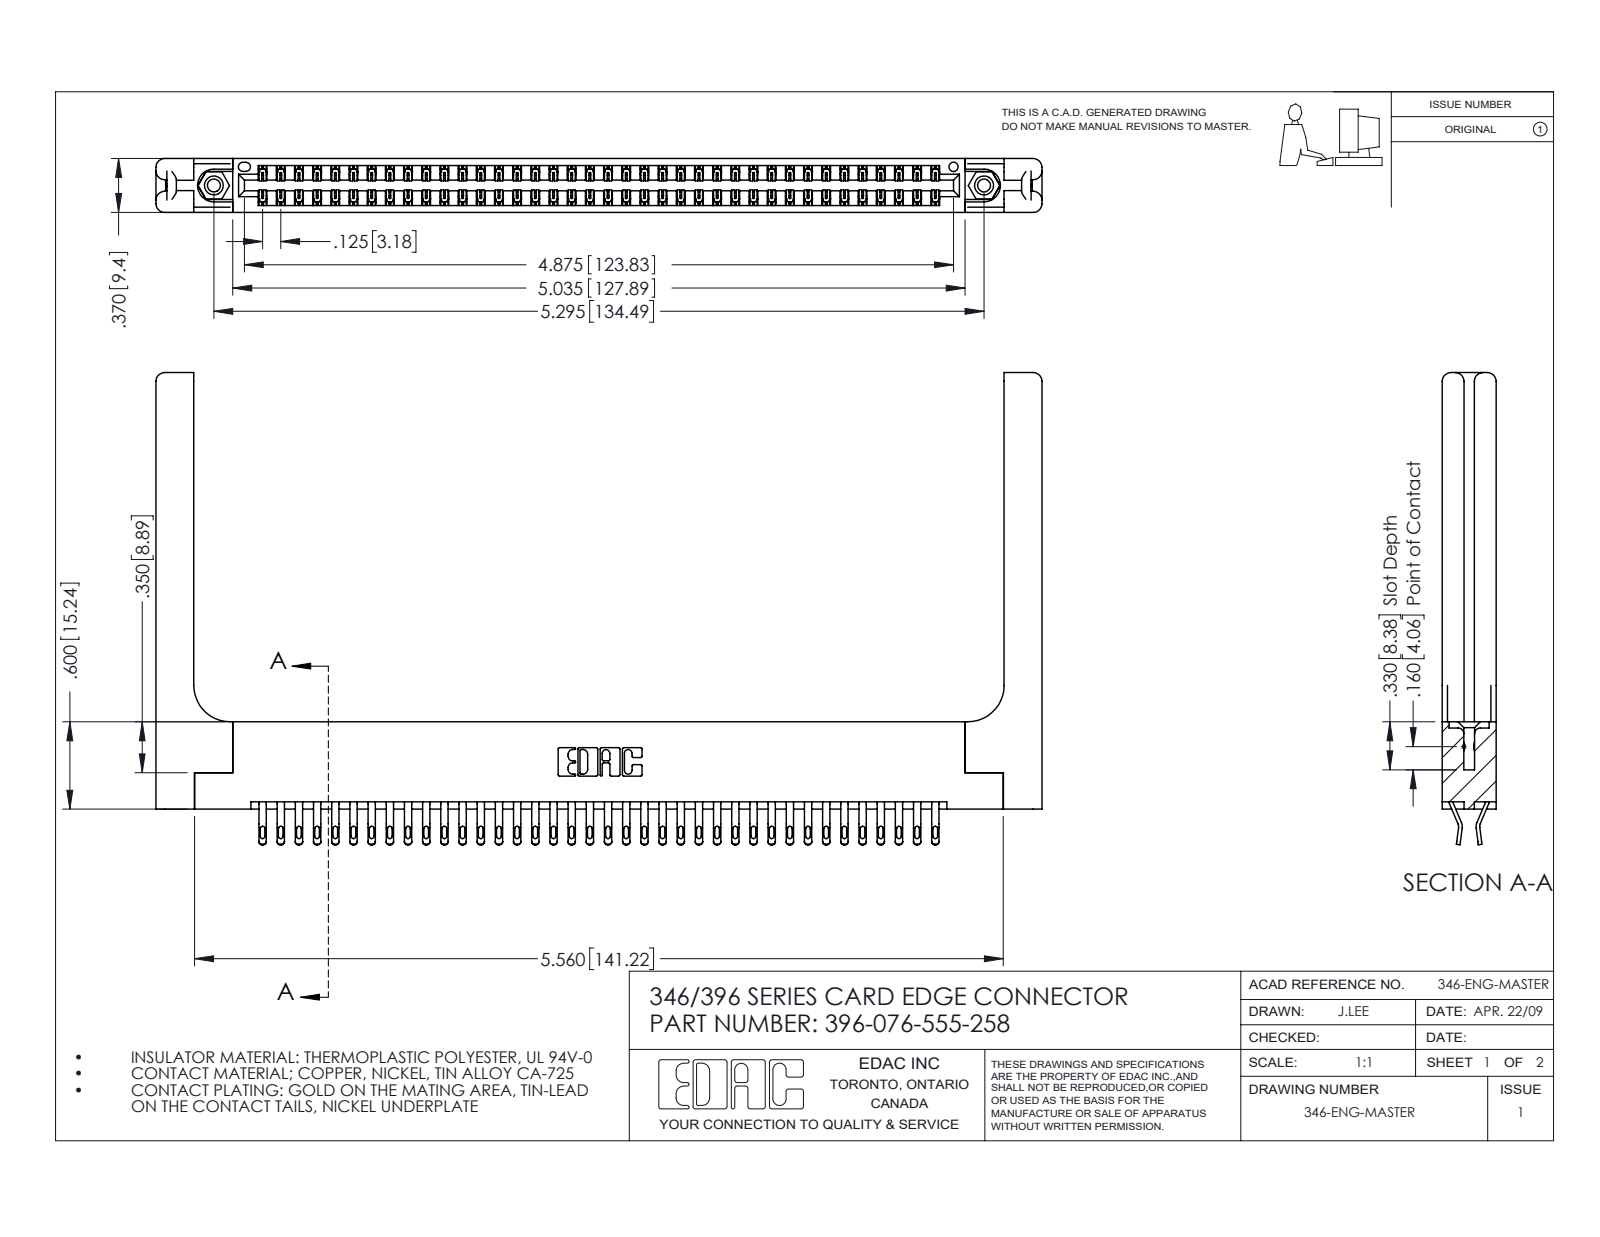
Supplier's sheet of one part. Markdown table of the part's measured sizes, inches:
| quantity | value |
| --- | --- |
| part name | 396-076-555-258; 345-250-001_345-250-001-102; 345-292-001_555 Tail; 346 Part_Flush Mounting Lugs - 0.156 Dia-TH (+1 more) |
| STEP written by | SolidWorks 2016 (CONFIG_CONTROL_DESIGN) |
| units | inches |
| bodies | 81 solids, 4786 faces (2732 planar, 1994 cylindrical, 60 other) |
| overall size | 6.091 × 3.245 × 0.37 |
| volume | 1.39 in³ |
| surface area | 41.37 in² |
| round holes (diameter × count) | 0.089 × 2, 0.125 × 2, 0.156 × 2, 0.064 × 1 |
| round bosses / shafts (diameter × count) | 0.155 × 2 |
| partial cylindrical surfaces (radius × count) | 0.016 × 152, 0.02 × 152, 0.006 × 114, 0.01 × 22, 0.06 × 16, 0.007 × 6, 0.031 × 6, 0.026 × 3 |
| main face-to-face distances | 0.37, 0.048, 0.322, 0.072, 0.148, 0.15, 0.25, 0.025, 0.298, 0.275 |
| hole center spacings | 0.246, 5.086, 5.295 |
